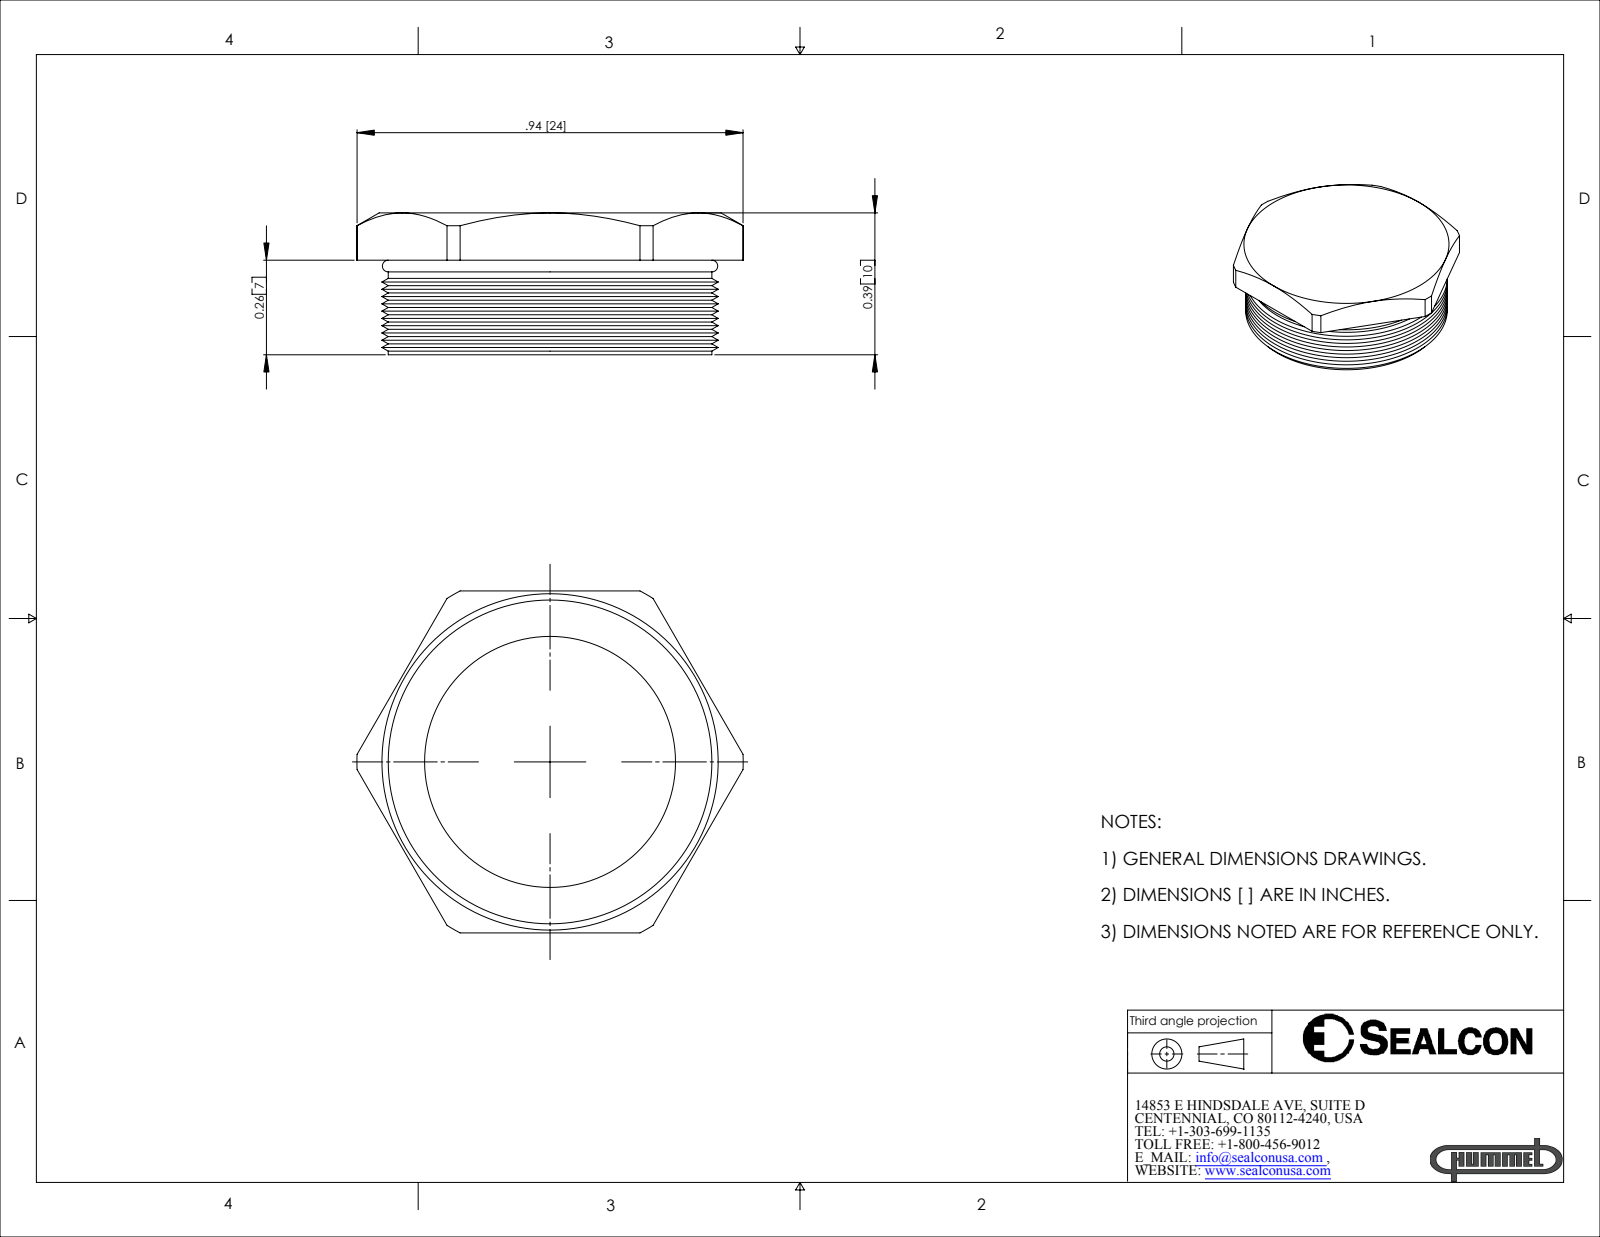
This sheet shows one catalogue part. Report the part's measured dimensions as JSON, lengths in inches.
{"part_name": "HP-16-SS-B", "step_written_by": "SolidWorks 2007 (CONFIG_CONTROL_DESIGN)", "units": "inches", "bodies": {"solids": 1, "faces": 88, "planar": 10, "cylindrical": 30, "other": 48}, "overall_size": [1.062, 0.94, 0.391], "volume_in3": 0.169, "surface_area_in2": 3.843, "round_holes": [[0.69, 1]], "round_bosses_or_shafts": [[0.89, 1]], "partial_cylinders_radius": [[0.531, 1]], "face_to_face_distances": [0.13, 0.26, 0.39, 0.94]}
